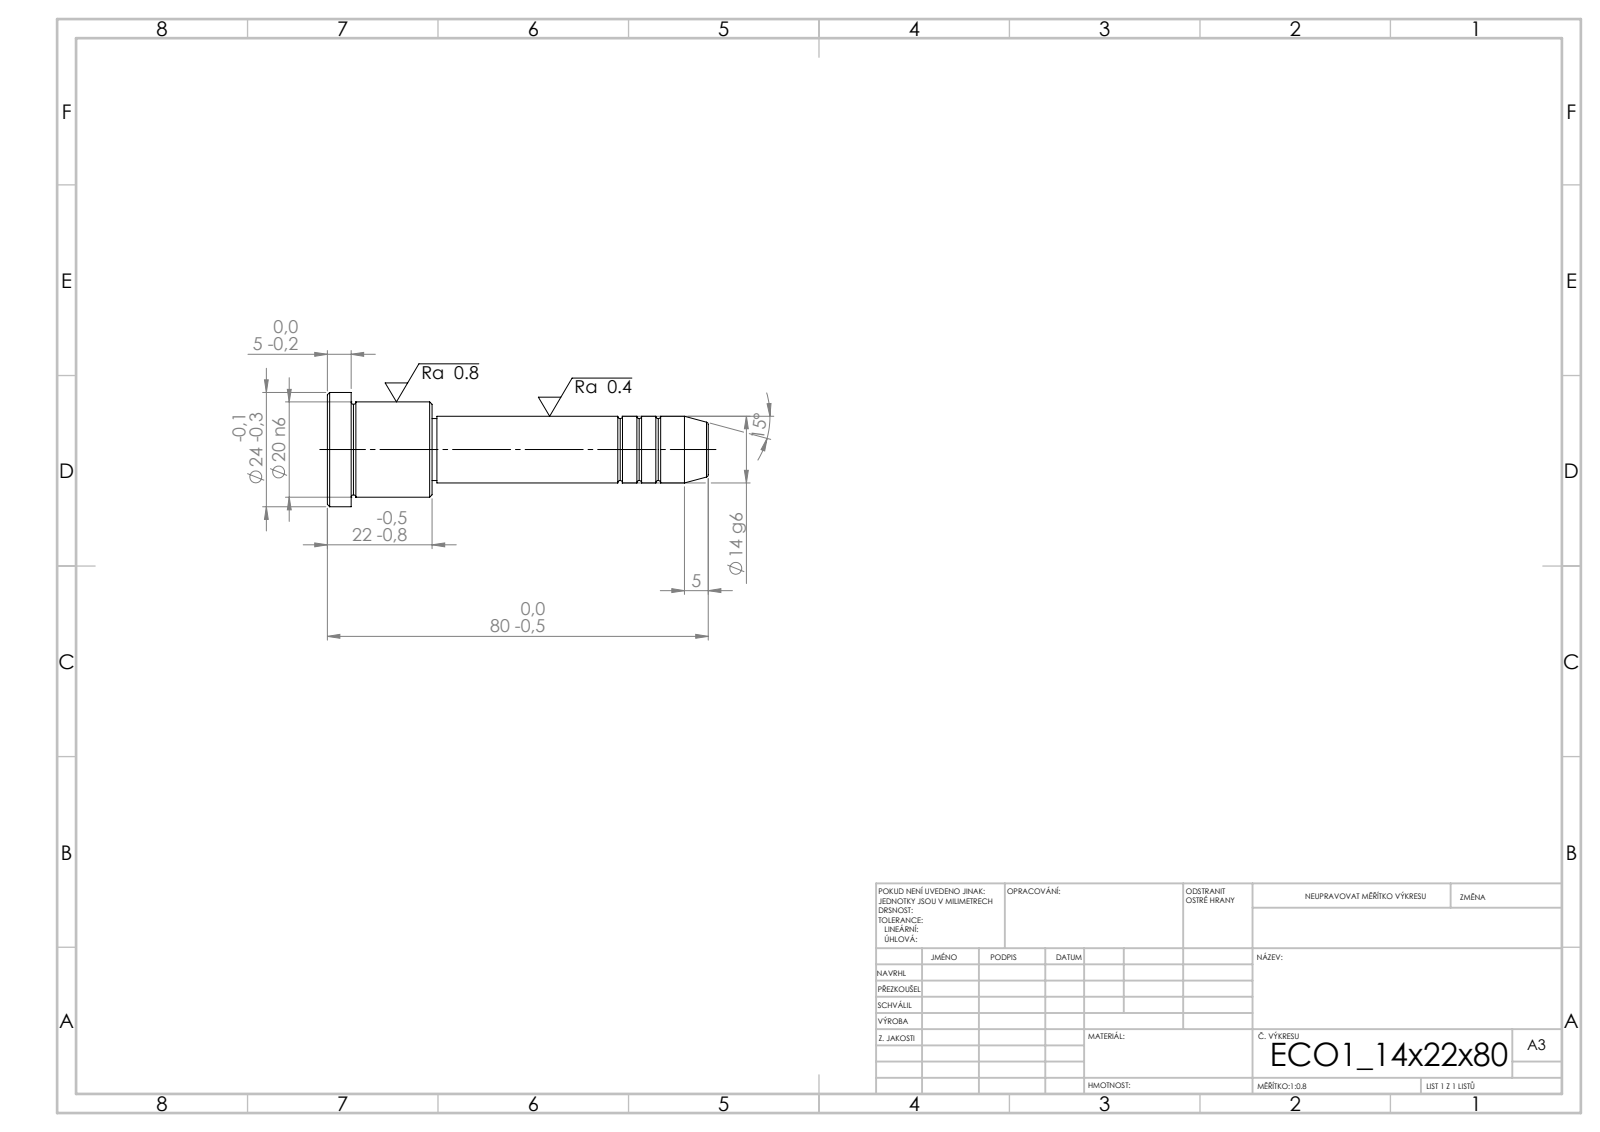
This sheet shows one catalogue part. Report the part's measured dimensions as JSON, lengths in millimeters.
{"step_written_by": "SolidWorks 2019 (CONFIG_CONTROL_DESIGN)", "units": "millimeters", "bodies": {"solids": 1, "faces": 43, "planar": 5, "cylindrical": 14, "other": 24}, "overall_size": [80, 24, 24], "volume_mm3": 16280, "surface_area_mm2": 4926, "round_bosses_or_shafts": [[24, 1], [20, 1], [14, 1], [13, 1]], "face_to_face_distances": [22, 17, 5, 58, 75, 80, 57, 1, 18, 23]}
